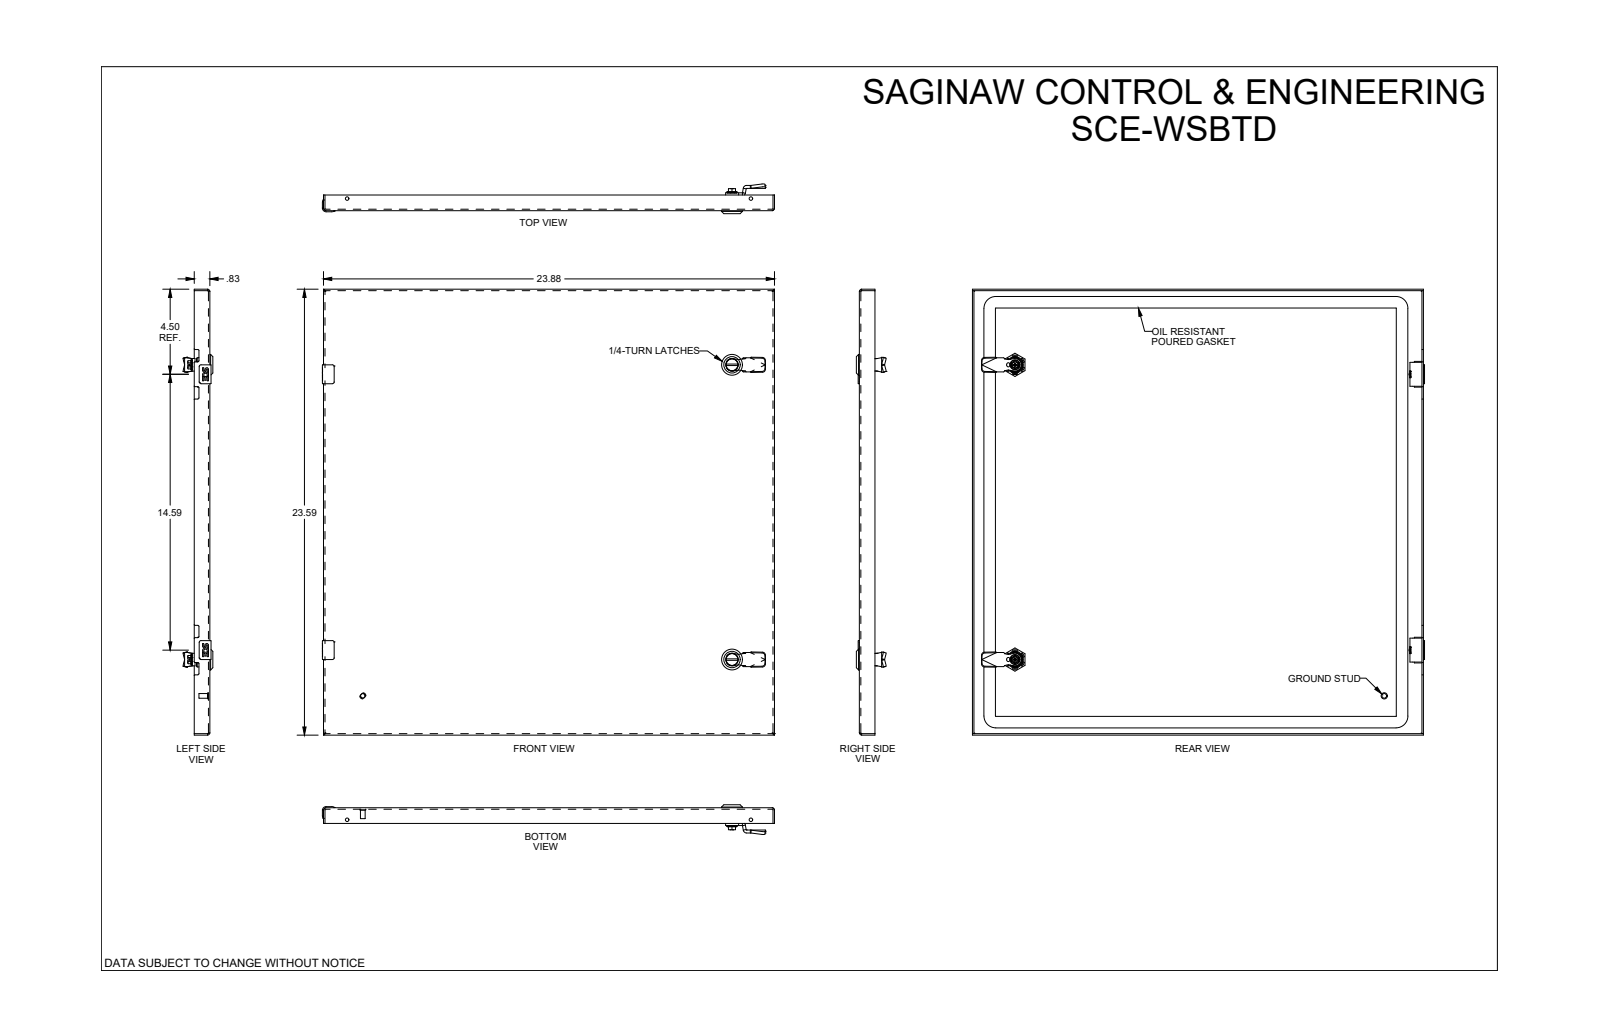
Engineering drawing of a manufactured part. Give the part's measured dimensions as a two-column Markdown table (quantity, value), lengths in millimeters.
| quantity | value |
| --- | --- |
| part name | SCE-WSBTD |
| STEP written by | SolidWorks 2021 (AUTOMOTIVE_DESIGN) |
| units | millimeters |
| bodies | 31 solids, 1525 faces (760 planar, 529 cylindrical, 236 other) |
| overall size | 607.9 × 599.3 × 40 |
| volume | 1 096 000 mm³ |
| surface area | 963 200 mm² |
| round holes (diameter × count) | 4.4 × 4, 5.2 × 4, 6.2 × 4, 9.5 × 4, 1 × 2, 5 × 2, 5.5 × 2, 8 × 2, 10 × 2, 16.1 × 2, 20.4 × 2, 5.2 × 1 |
| round bosses / shafts (diameter × count) | 4.3 × 6, 6.4 × 4, 6.1 × 4, 5 × 3, 28 × 2, 19.8 × 2, 16 × 2, 13.5 × 2 |
| partial cylindrical surfaces (radius × count) | 0.3 × 56, 0.4 × 24, 0.5 × 20, 0.6 × 8, 1.6 × 8, 2.5 × 8, 4 × 8, 5.6 × 8 |
| main face-to-face distances | 2, 597.3, 604.4, 599.3, 595.3, 606.4, 602.5, 7.1, 9.1, 11.9 |
| hole center spacings | 12.5, 12.5, 25, 358.2, 370.7, 370.7, 383.2, 531.2 |
